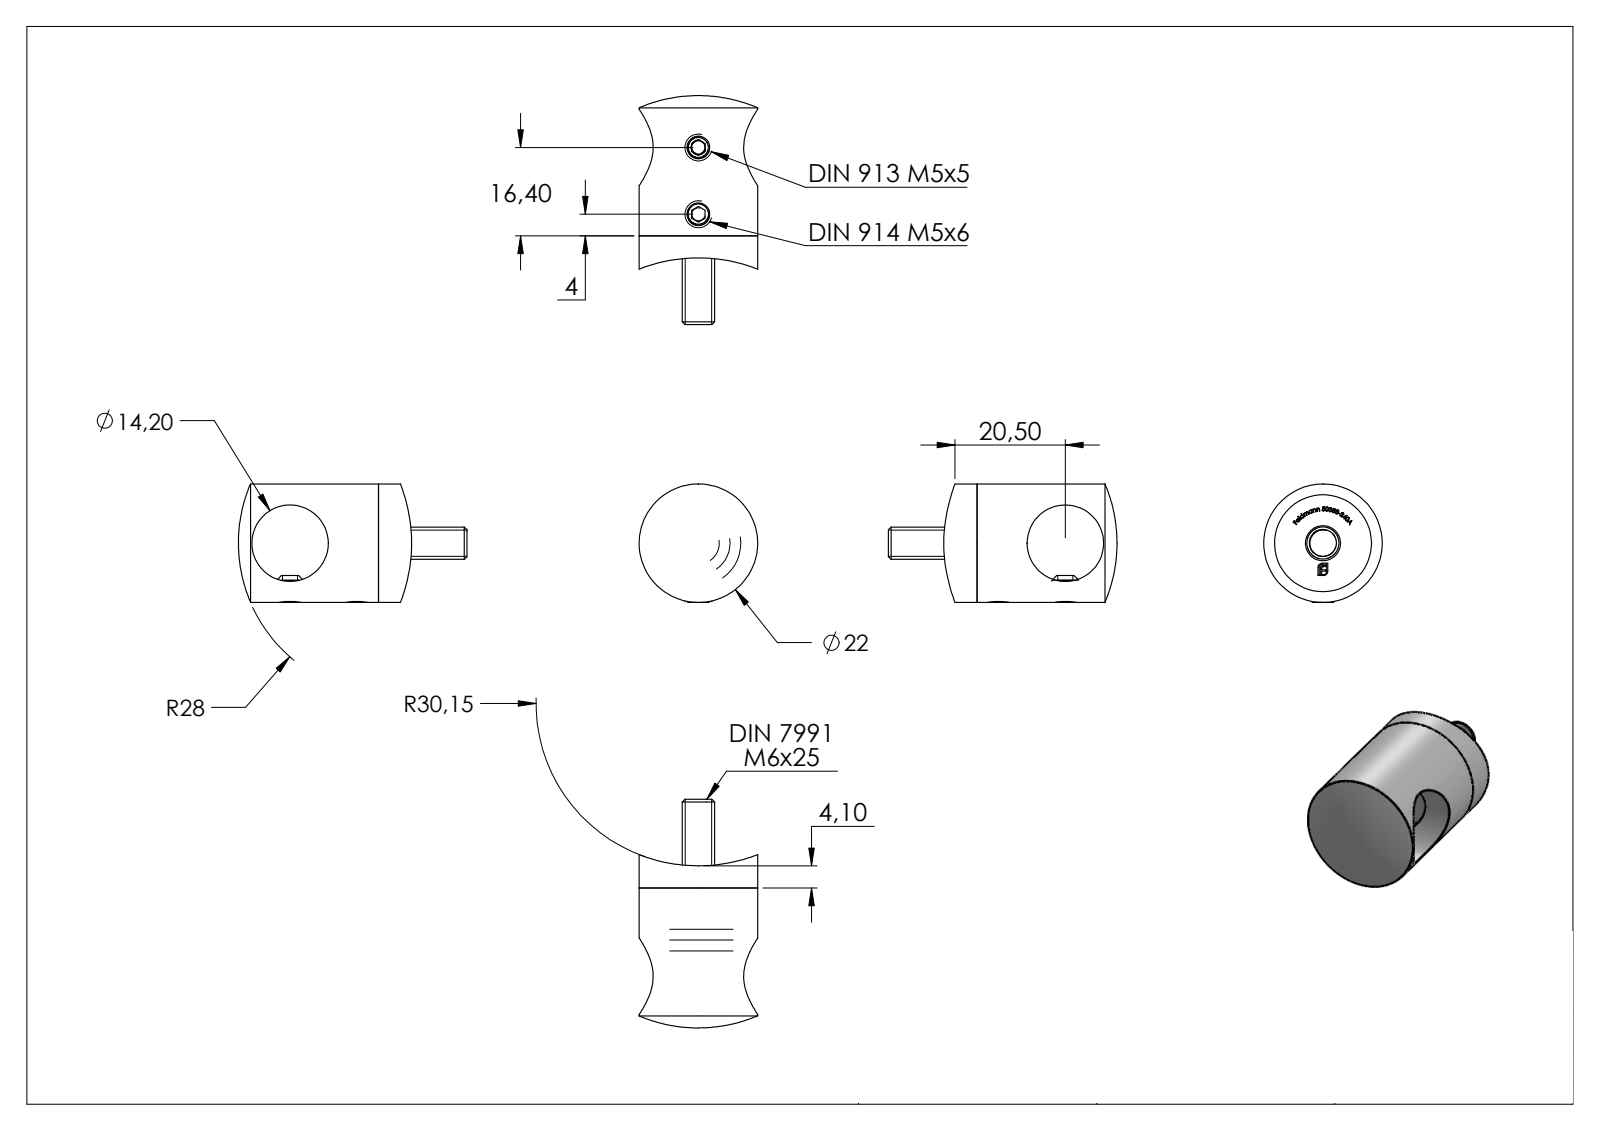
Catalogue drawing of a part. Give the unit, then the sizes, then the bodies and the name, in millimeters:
Units: millimetres
Overall size (bounding box): 71 × 42.45 × 22
Round holes (diameter × count): ⌀4.2 ×2, ⌀6.5 ×1, ⌀12 ×1, ⌀14.2 ×1, ⌀18 ×1
Round bosses / shafts (diameter × count): ⌀5 ×2, ⌀22 ×1, ⌀11.9 ×1, ⌀6 ×1
Partial cylindrical surfaces — rounded edges, fillets, slot ends (radius × count): R30.15 ×1
Main face-to-face distances: 2.1, 10.65, 8.55, 2.5, 1.05, 9.6, 7.5, 14.35, 16.45, 23.95
Hole centre spacings: 12.4
Volume: 7 449 mm³ · Surface area: 5 831 mm²
Bodies: 5 solids, 360 faces (184 planar, 15 cylindrical, 161 other)
Part name (STEP PRODUCT): DIN914_DIN 914 M5x6; 50388-240A; DIN 7991 Konfig_M6x25; DIN914 (+7 more)
STEP written by: SolidWorks 2018 (CONFIG_CONTROL_DESIGN)
